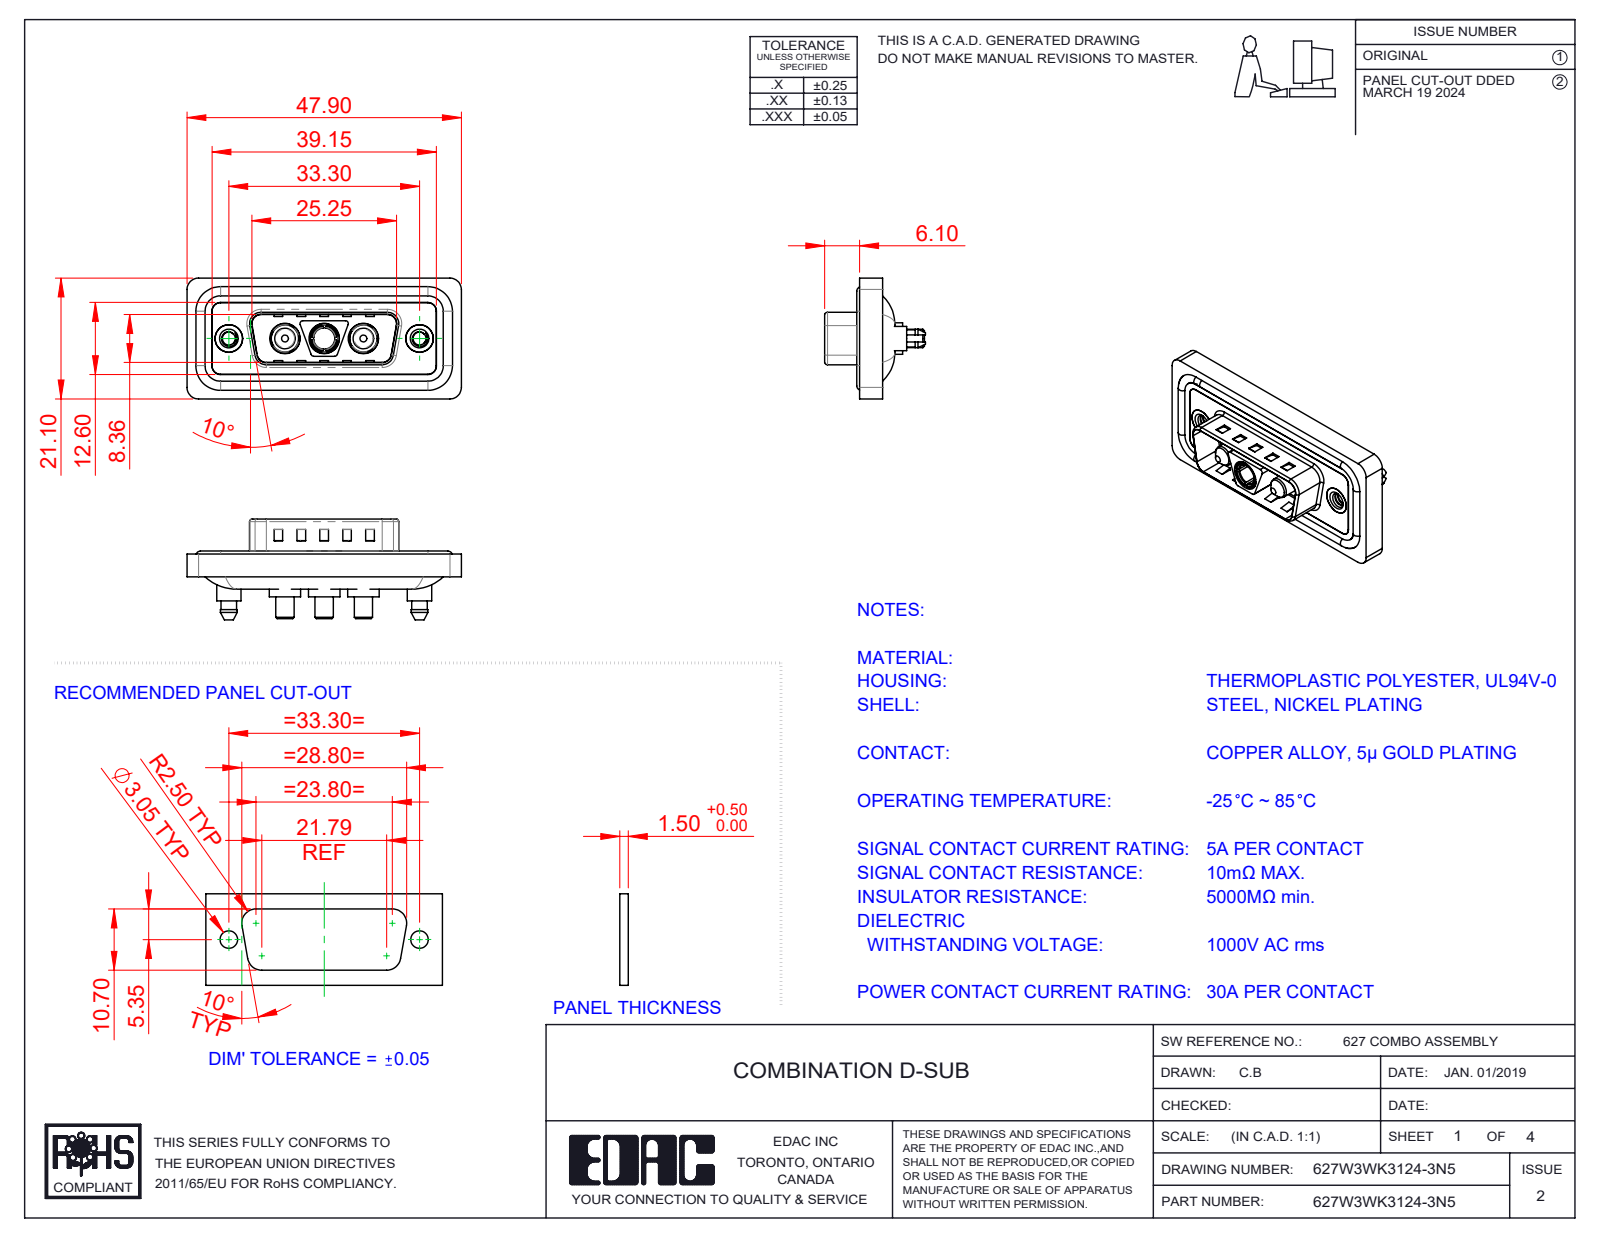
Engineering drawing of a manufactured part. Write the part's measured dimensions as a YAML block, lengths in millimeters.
part_name: "Power Socket_30A S; 627Combo Shell Front_15 Contacts; 627Combo Waterproof Housing_15 Contacts; 627W3WK3124-3N5 (+4 more)"
step_written_by: "SolidWorks 2023 (CONFIG_CONTROL_DESIGN)"
units: millimeters
bodies: {solids: 13, faces: 659, planar: 247, cylindrical: 282, other: 130}
overall_size: [47.9, 21.1, 17.6]
volume: 5843
surface_area: 9474
round_holes:
  - {diameter: 4.85, count: 3}
  - {diameter: 5.3, count: 3}
  - {diameter: 2.26, count: 2}
  - {diameter: 4, count: 2}
  - {diameter: 4.8, count: 2}
  - {diameter: 5, count: 2}
  - {diameter: 3.7, count: 1}
round_bosses_or_shafts:
  - {diameter: 1.6, count: 4}
  - {diameter: 5.5, count: 3}
  - {diameter: 5.2, count: 3}
  - {diameter: 4.75, count: 3}
  - {diameter: 3.75, count: 3}
  - {diameter: 3.2, count: 3}
  - {diameter: 5.4, count: 2}
  - {diameter: 4.9, count: 2}
partial_cylinders:
  - {radius: 1.5, count: 28}
  - {radius: 2, count: 20}
  - {radius: 0.5, count: 12}
  - {radius: 1.6, count: 10}
  - {radius: 0.25, count: 4}
  - {radius: 0.6, count: 4}
  - {radius: 0.65, count: 4}
  - {radius: 0.9, count: 4}
face_to_face_distances: [0.4, 1.1, 1.5, 0.5, 3.1, 1.6, 2.9, 4, 0.7, 0.82]
hole_center_spacings: [6.85, 9.8, 16.65, 23.5, 13.7, 33.3]
